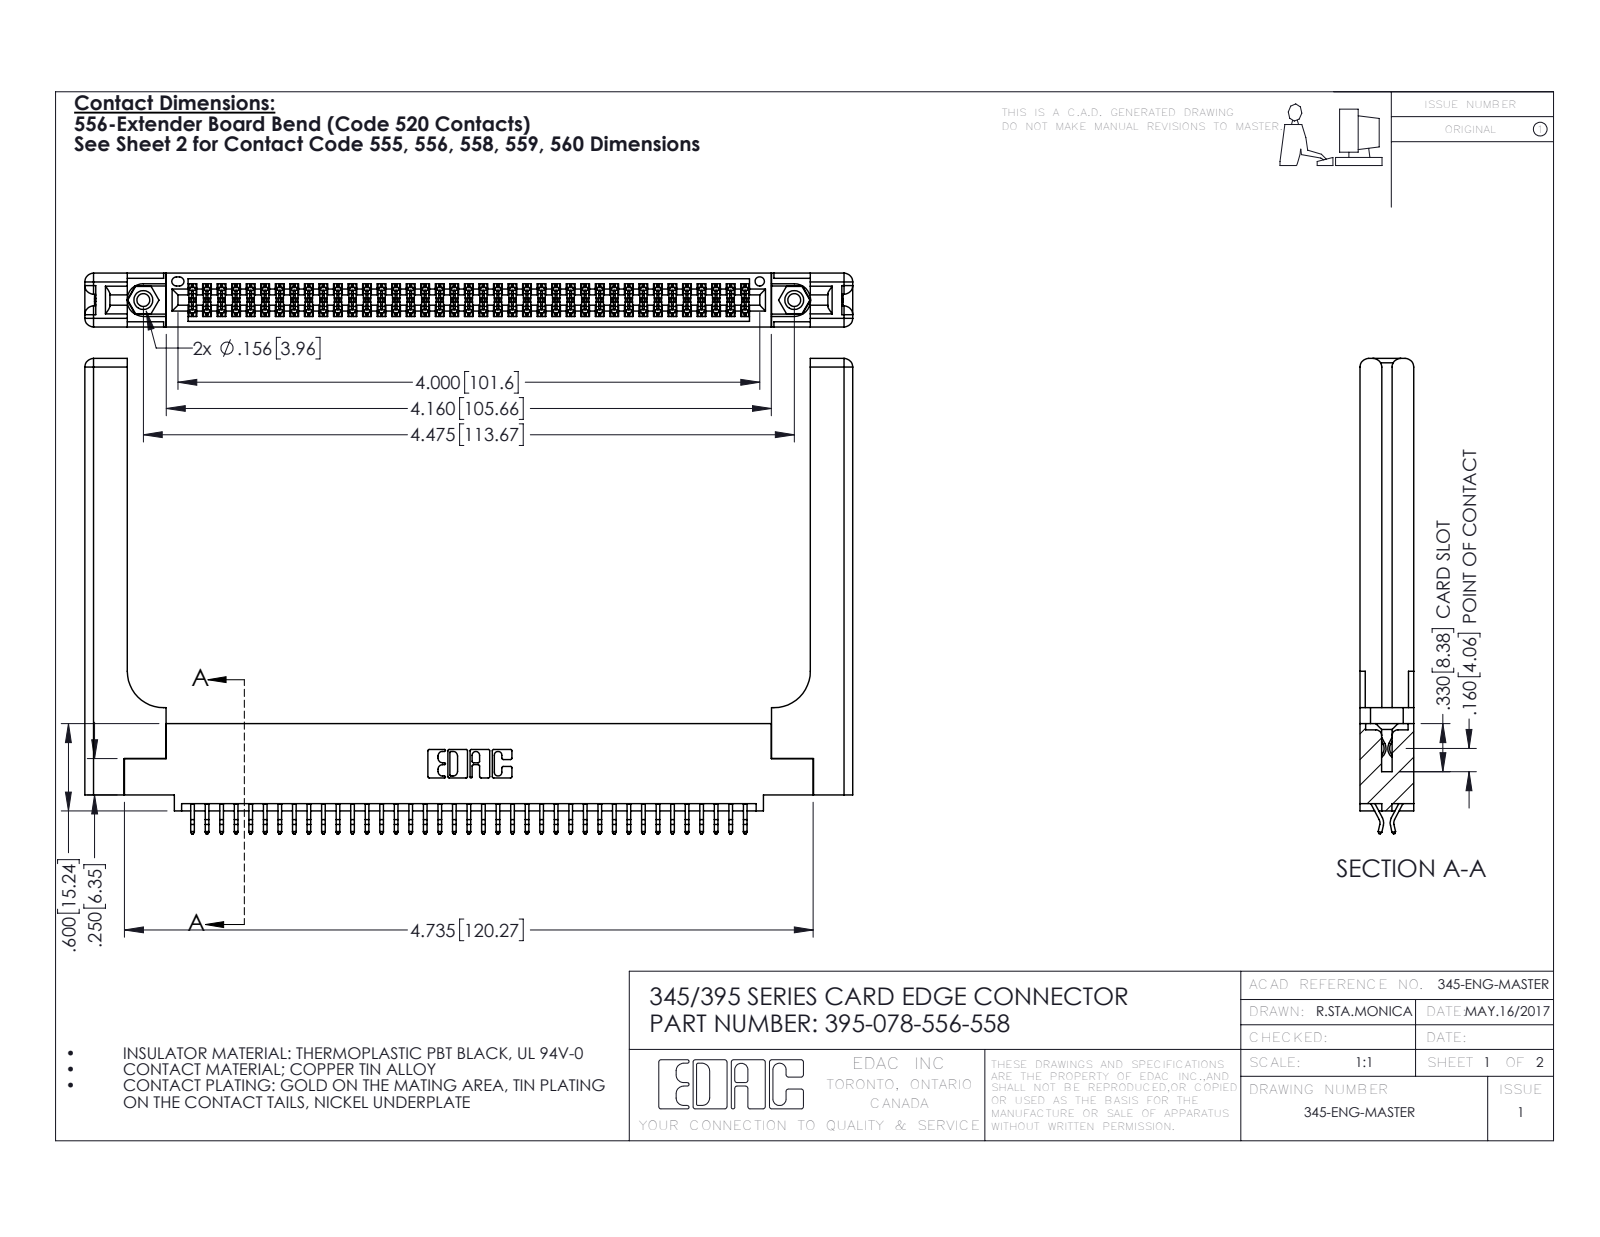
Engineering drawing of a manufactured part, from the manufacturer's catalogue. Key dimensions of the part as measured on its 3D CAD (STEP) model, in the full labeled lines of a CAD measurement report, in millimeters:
Part name (STEP PRODUCT): 345-220-058_345-220-058; 345-250-001_345-250-001-102; 345 Part_0.110 Offset - 0.156 Dia-TH; 395-078-556-558 (+1 more)
STEP written by: SolidWorks 2016 (CONFIG_CONTROL_DESIGN)
Units: millimetres
Bodies: 83 solids, 4754 faces (3118 planar, 1576 cylindrical, 60 other)
Overall size (bounding box): 134.1 × 83 × 9.4
Volume: 21 400 mm³ · Surface area: 24 120 mm²
Round holes (diameter × count): ⌀2.3 ×2, ⌀3.2 ×2, ⌀4 ×2, ⌀1.6 ×1
Round bosses / shafts (diameter × count): ⌀3.9 ×2
Partial cylindrical surfaces — rounded edges, fillets, slot ends (radius × count): R0.2 ×117, R0.3 ×22, R1.5 ×16, R0.2 ×6, R0.8 ×6, R0.7 ×3, R0.3 ×2, R0.4 ×2
Main face-to-face distances: 1.8, 9.4, 7.6, 0.6, 5.1, 2.5, 6.9, 5.7, 3.8, 3.8
Hole centre spacings: 6.9, 107.7, 113.7
